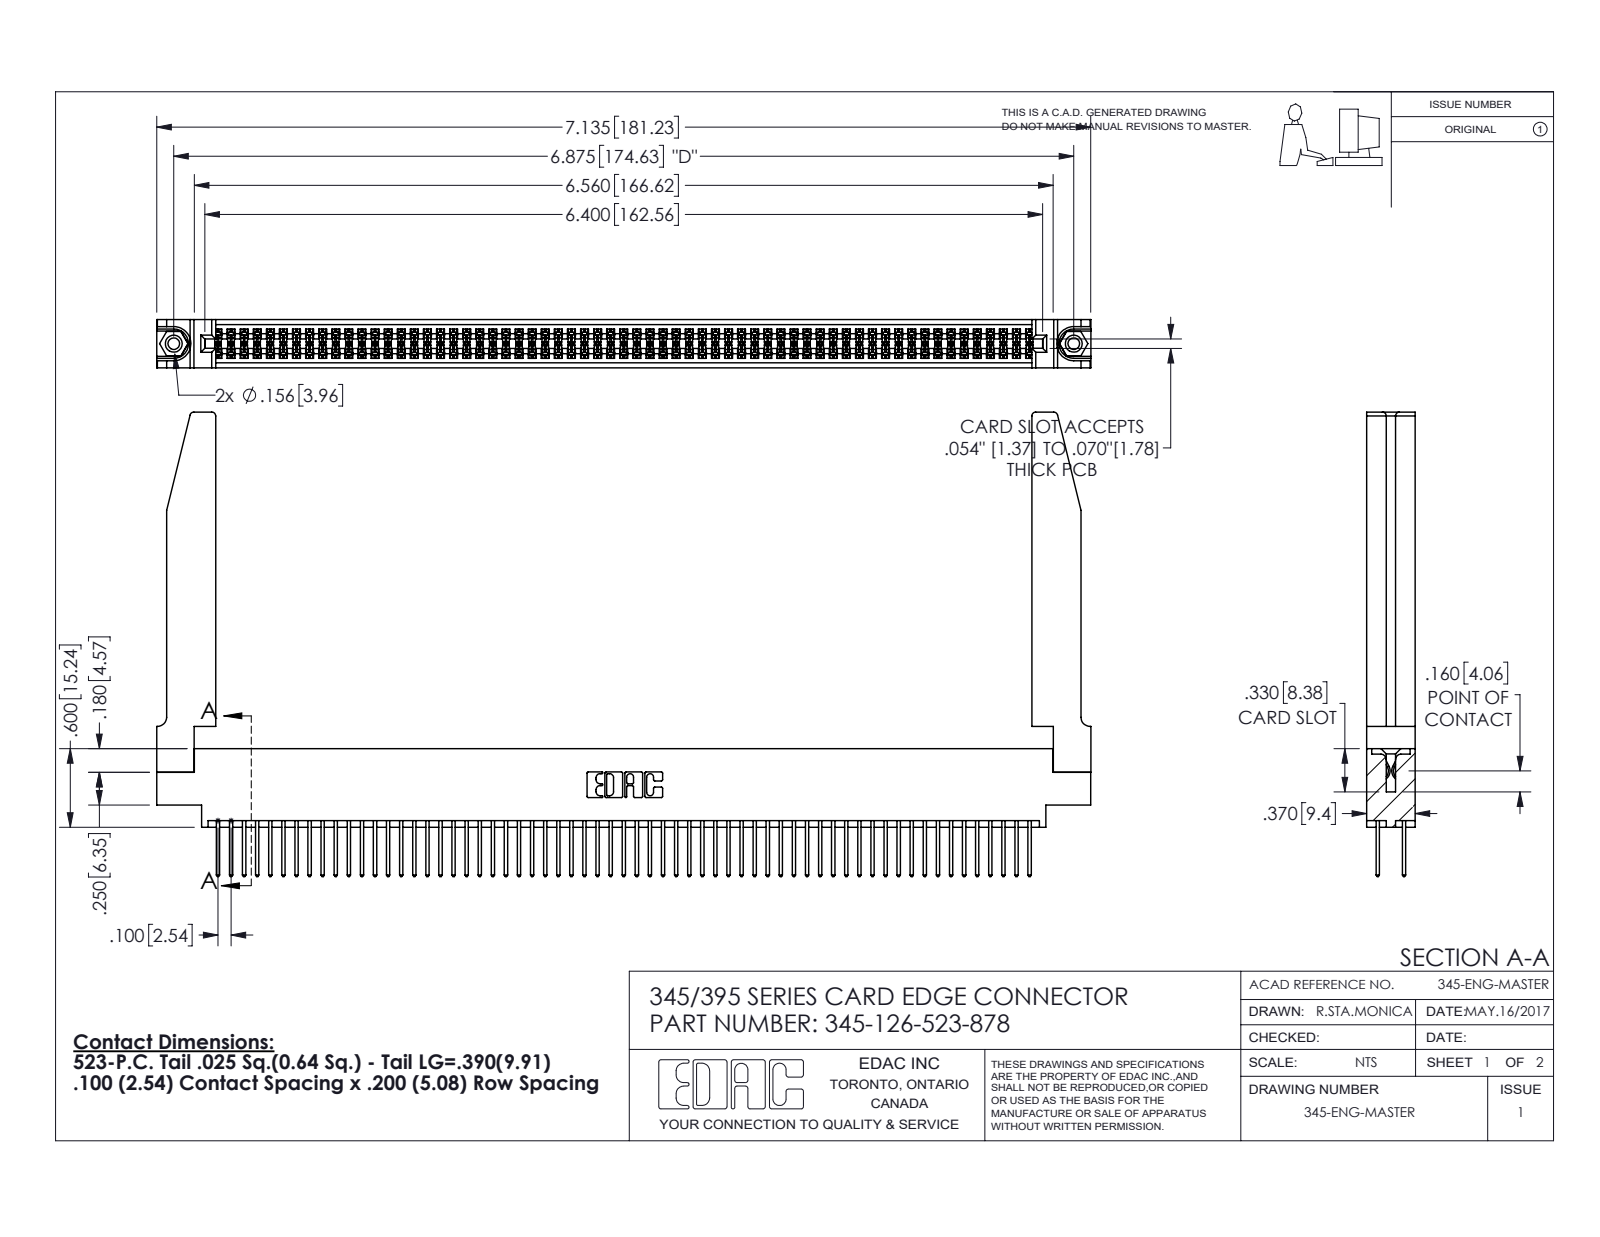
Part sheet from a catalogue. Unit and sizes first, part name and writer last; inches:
Units: inches
Overall size (bounding box): 7.136 × 3.547 × 0.37
Round holes (diameter × count): ⌀0.089 ×2, ⌀0.125 ×2, ⌀0.156 ×2, ⌀0.064 ×1
Round bosses / shafts (diameter × count): ⌀0.155 ×2
Partial cylindrical surfaces — rounded edges, fillets, slot ends (radius × count): R0.006 ×189, R0.01 ×126, R0.01 ×22, R0.03 ×8, R0.007 ×6, R0.031 ×6, R0.026 ×3, R0.014 ×2
Main face-to-face distances: 0.072, 0.298, 0.37, 0.098, 0.272, 0.025, 0.2, 0.225, 0.175, 0.148
Hole centre spacings: 0.27, 6.639, 6.875
Volume: 1.569 in³ · Surface area: 54.37 in²
Bodies: 131 solids, 6664 faces (4384 planar, 2228 cylindrical, 52 other)
Part name (STEP PRODUCT): 345-126-523-878; 345-220-078_345-220-078; 345-292-001_345-293-123; 345-250-001_345-250-001-102 (+1 more)
STEP written by: SolidWorks 2016 (CONFIG_CONTROL_DESIGN)
